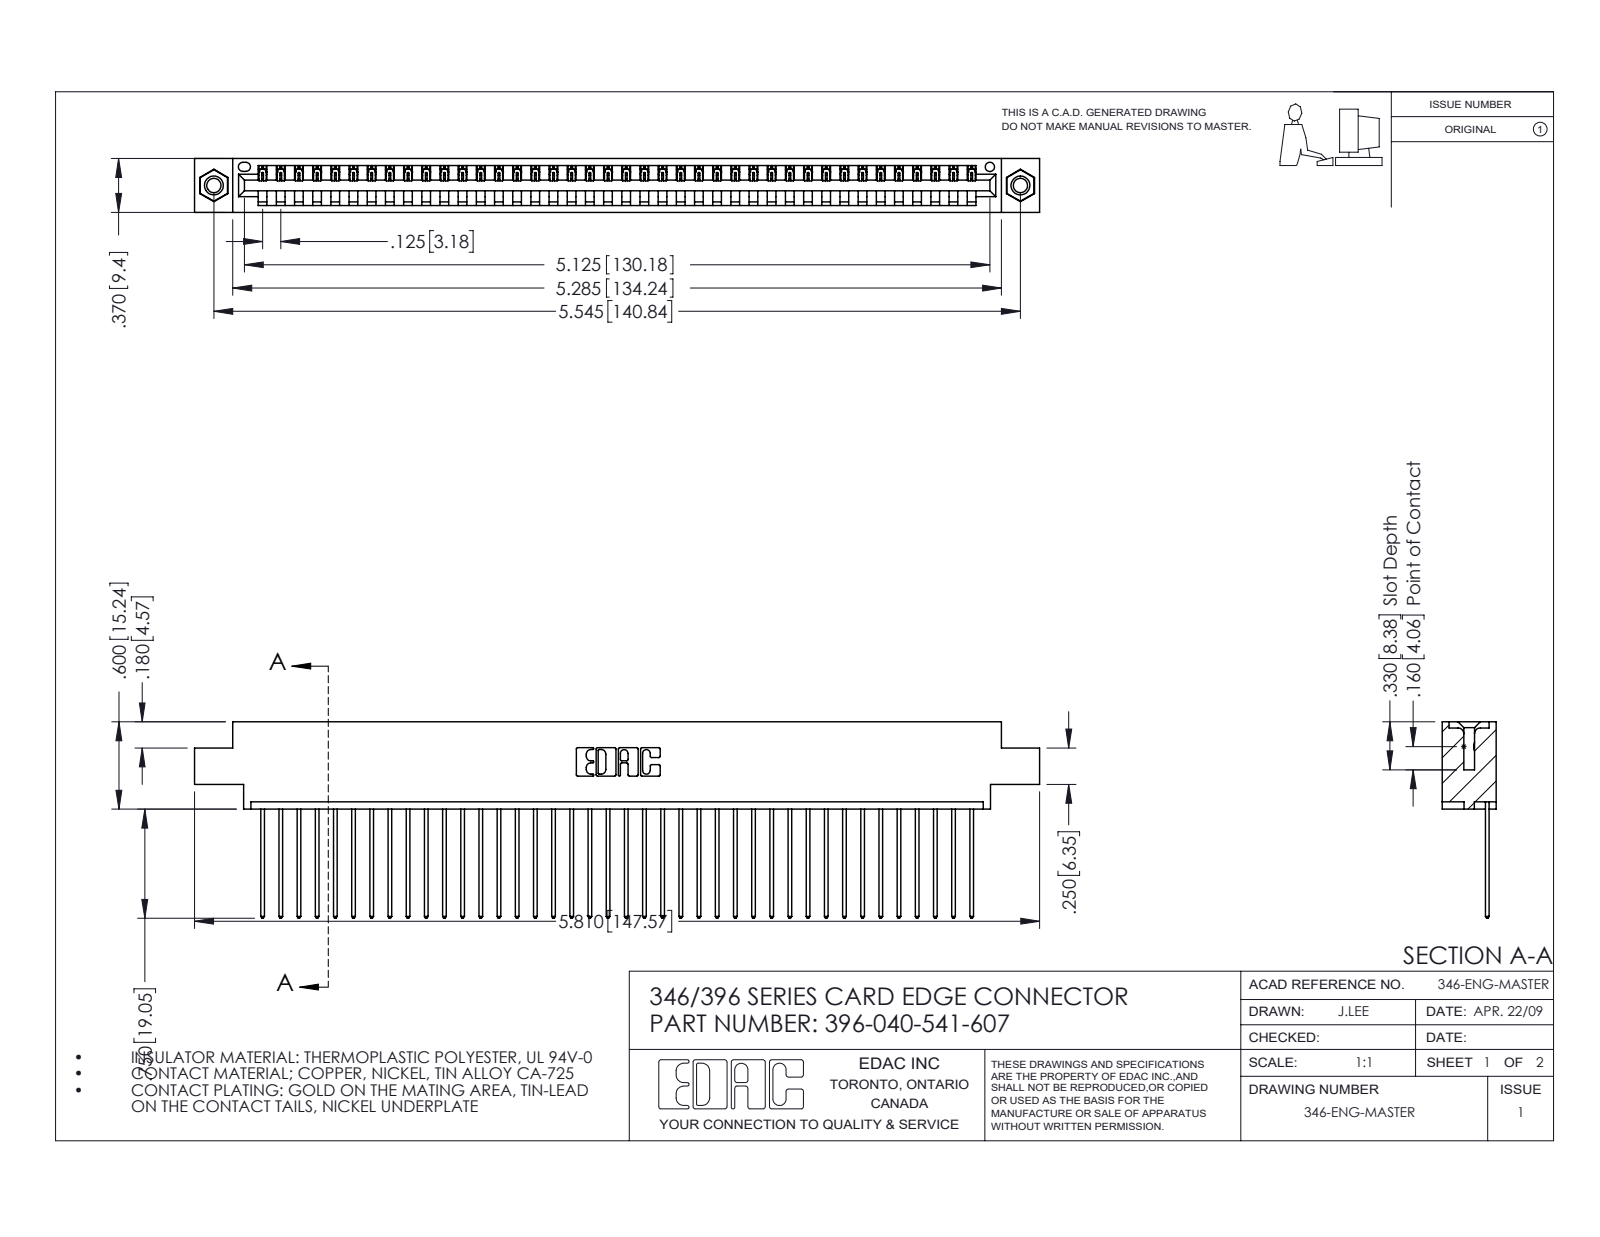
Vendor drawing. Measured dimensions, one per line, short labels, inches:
name: 345-292-001_345-293-141; 346 Part_0.170 Offset - 0.156 Dia-TI; 345-250-001_345-250-005-103; 396-040-541-607
written by: SolidWorks 2016 (CONFIG_CONTROL_DESIGN)
unit: in
bodies: 43 solids, 2506 faces (1712 planar, 778 cylindrical, 16 other)
size: 5.81 × 1.35 × 0.37
volume: 0.859 in³; area: 28.76 in²
holes: 2× ⌀0.098, 2× ⌀0.125, 2× ⌀0.156, 1× ⌀0.064
bosses: 2× ⌀0.155
rounds: 80× R0.006, 80× R0.01, 22× R0.01, 6× R0.007, 6× R0.031, 3× R0.026, 2× R0.031, 2× R0.04
face distances: 0.048, 0.322, 0.37, 0.25, 0.072, 0.298, 0.025, 0.222, 0.148, 0.1
hole spacings: 0.246, 5.336, 5.545
